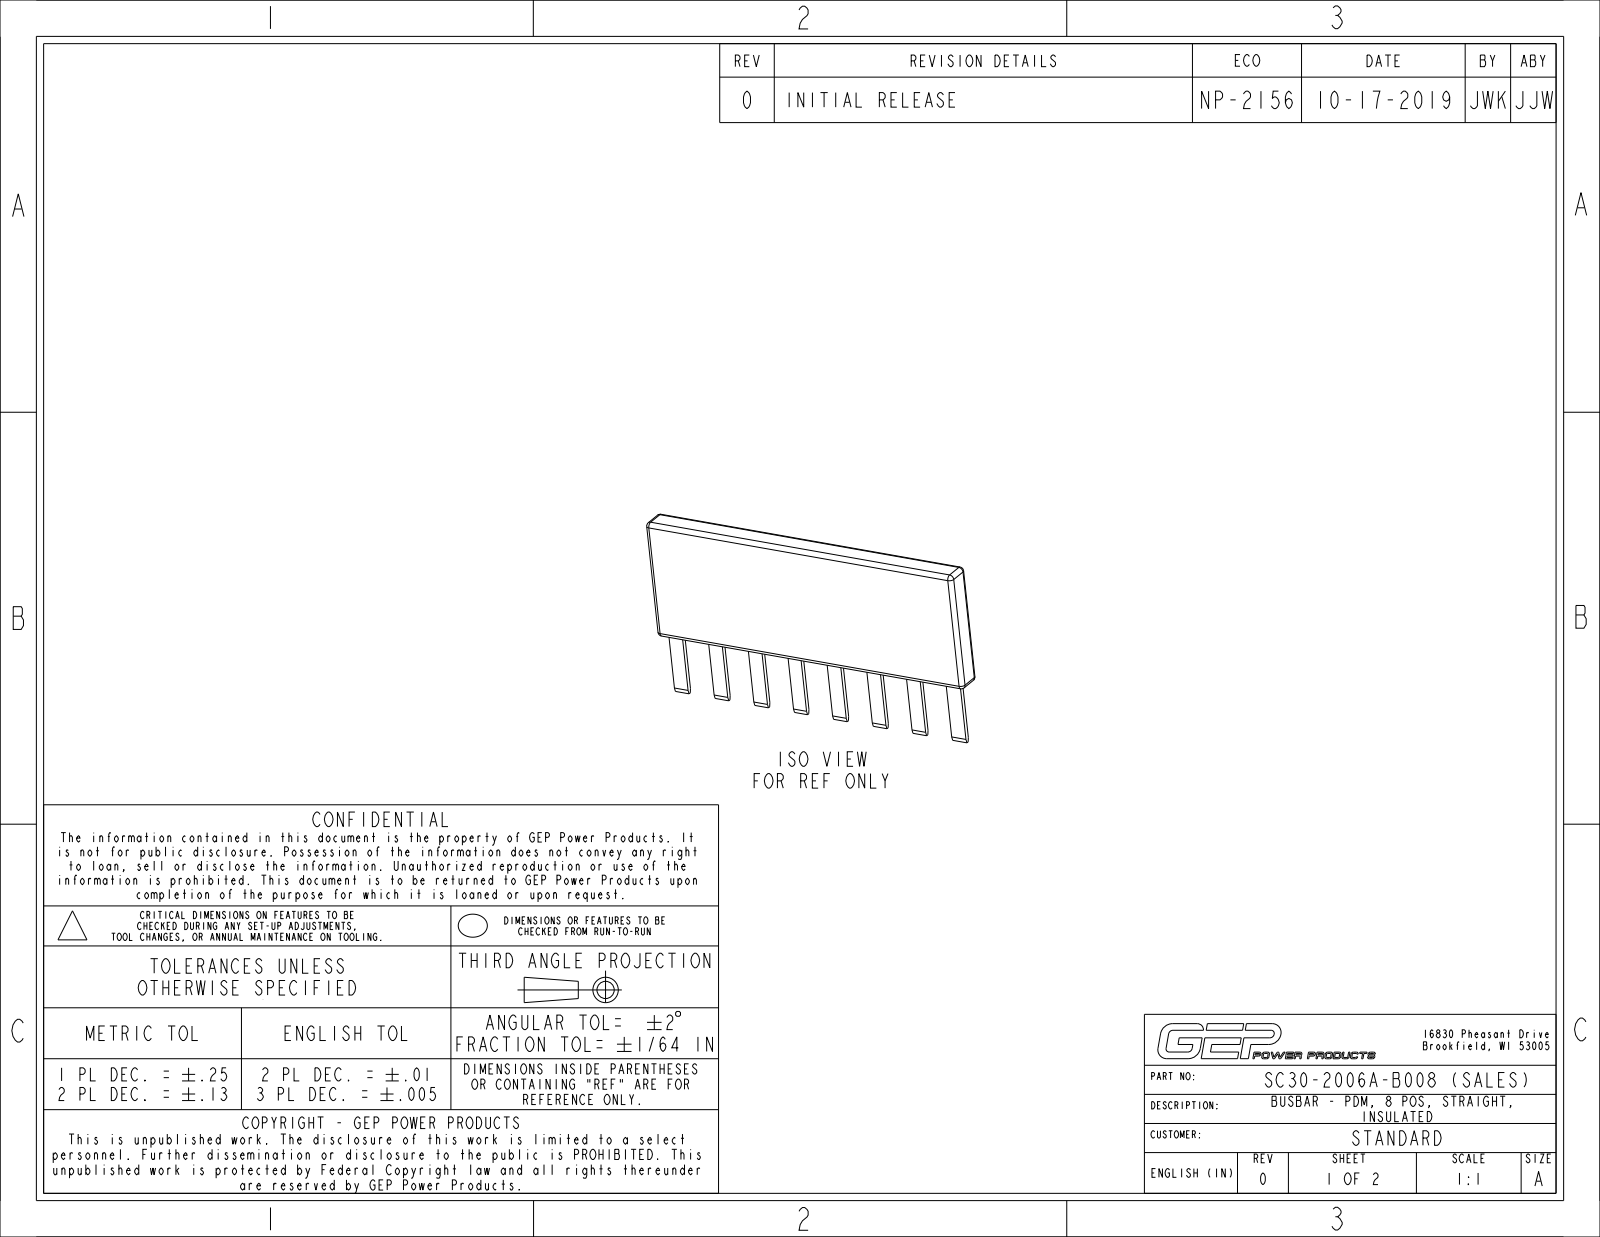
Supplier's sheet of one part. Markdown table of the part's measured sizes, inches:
| quantity | value |
| --- | --- |
| part name | PC29-2004A-C000_MOLD; PC29-2004A-C000_NCF; PC30-2006A-B008_NCF_ASM; SC30-2006A-B008_NCF_ASM |
| STEP written by | CREO PARAMETRIC BY PTC INC, 2017110 (CONFIG_CONTROL_DESIGN) |
| units | inches |
| bodies | 2 solids, 113 faces (91 planar, 14 cylindrical, 8 other) |
| overall size | 2.47 × 1.31 × 0.184 |
| volume | 0.405 in³ |
| surface area | 17.6 in² |
| partial cylindrical surfaces (radius × count) | 0.03 × 12, 0.032 × 1 |
| main face-to-face distances | 0.06, 0.124, 0.032, 0.032, 0.064, 0.092, 0.184, 0.092, 0.87, 0.06 |
